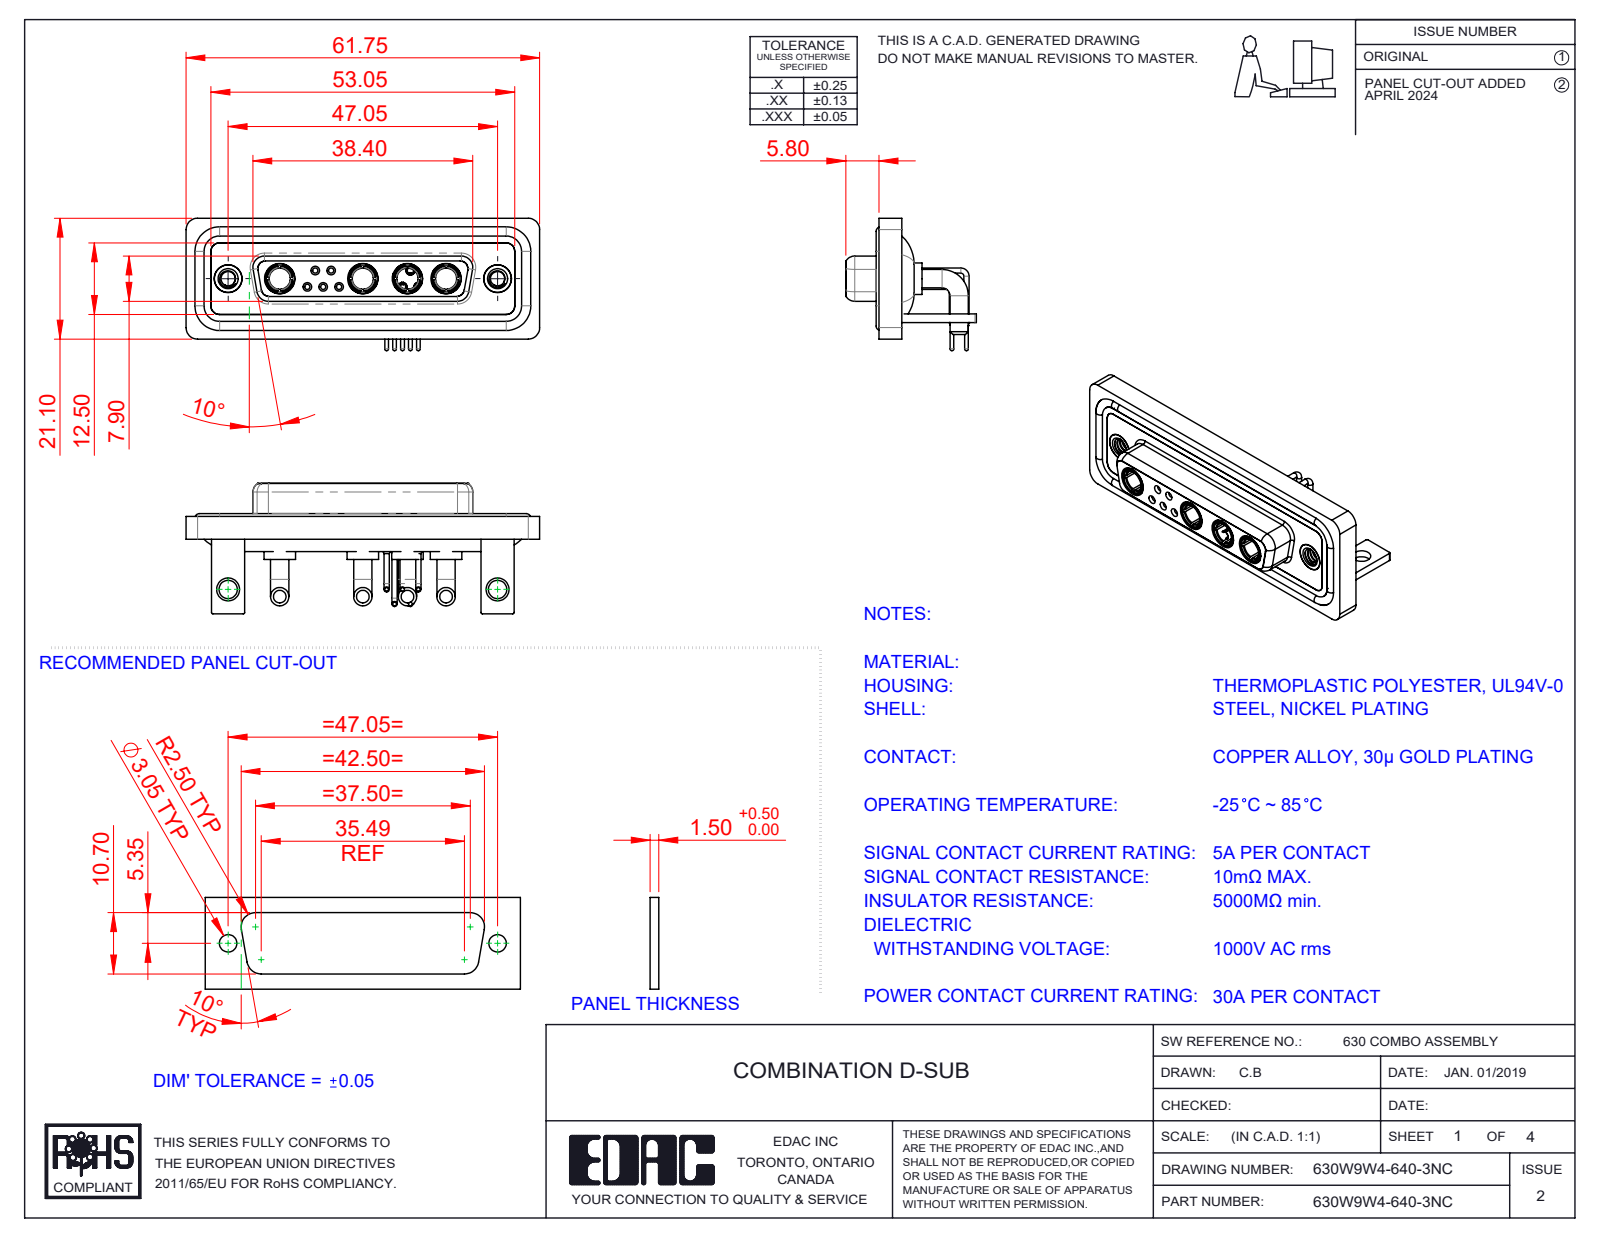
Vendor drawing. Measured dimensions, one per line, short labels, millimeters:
name: 630Combo Threaded Rivet_A; 630Combo Contact Row 1_50 Contacts; Power Socket_30A RA; 630Combo Shell Front_25 Contacts (+6 more)
written by: SolidWorks 2023 (CONFIG_CONTROL_DESIGN)
unit: mm
bodies: 22 solids, 1005 faces (316 planar, 425 cylindrical, 264 other)
size: 61.75 × 23.12 × 22.8
volume: 8 923 mm³; area: 14 859 mm²
holes: 6× ⌀4.85, 5× ⌀0.9, 5× ⌀1.1, 5× ⌀1.5, 5× ⌀2, 4× ⌀3.7, 4× ⌀5.3, 3× ⌀1.6, 2× ⌀1.7, 2× ⌀2.5, 2× ⌀3.2, 2× ⌀4
bosses: 10× ⌀0.9, 9× ⌀1.6, 8× ⌀3.2, 5× ⌀2, 5× ⌀1.5, 5× ⌀0.65, 4× ⌀5.5, 4× ⌀5.2
rounds: 19× R2, 18× R1.5, 16× R0.25, 8× R1.35, 8× R1.6, 5× R0.5, 4× R0.6, 4× R0.65
face distances: 0.4, 1.8, 2.9, 3.7, 1.5, 4.1, 1.1, 1.4, 1.6, 2.5
hole spacings: 3.16, 2.77, 5.04, 13.85, 11.08, 12.79, 15.5, 5.54
